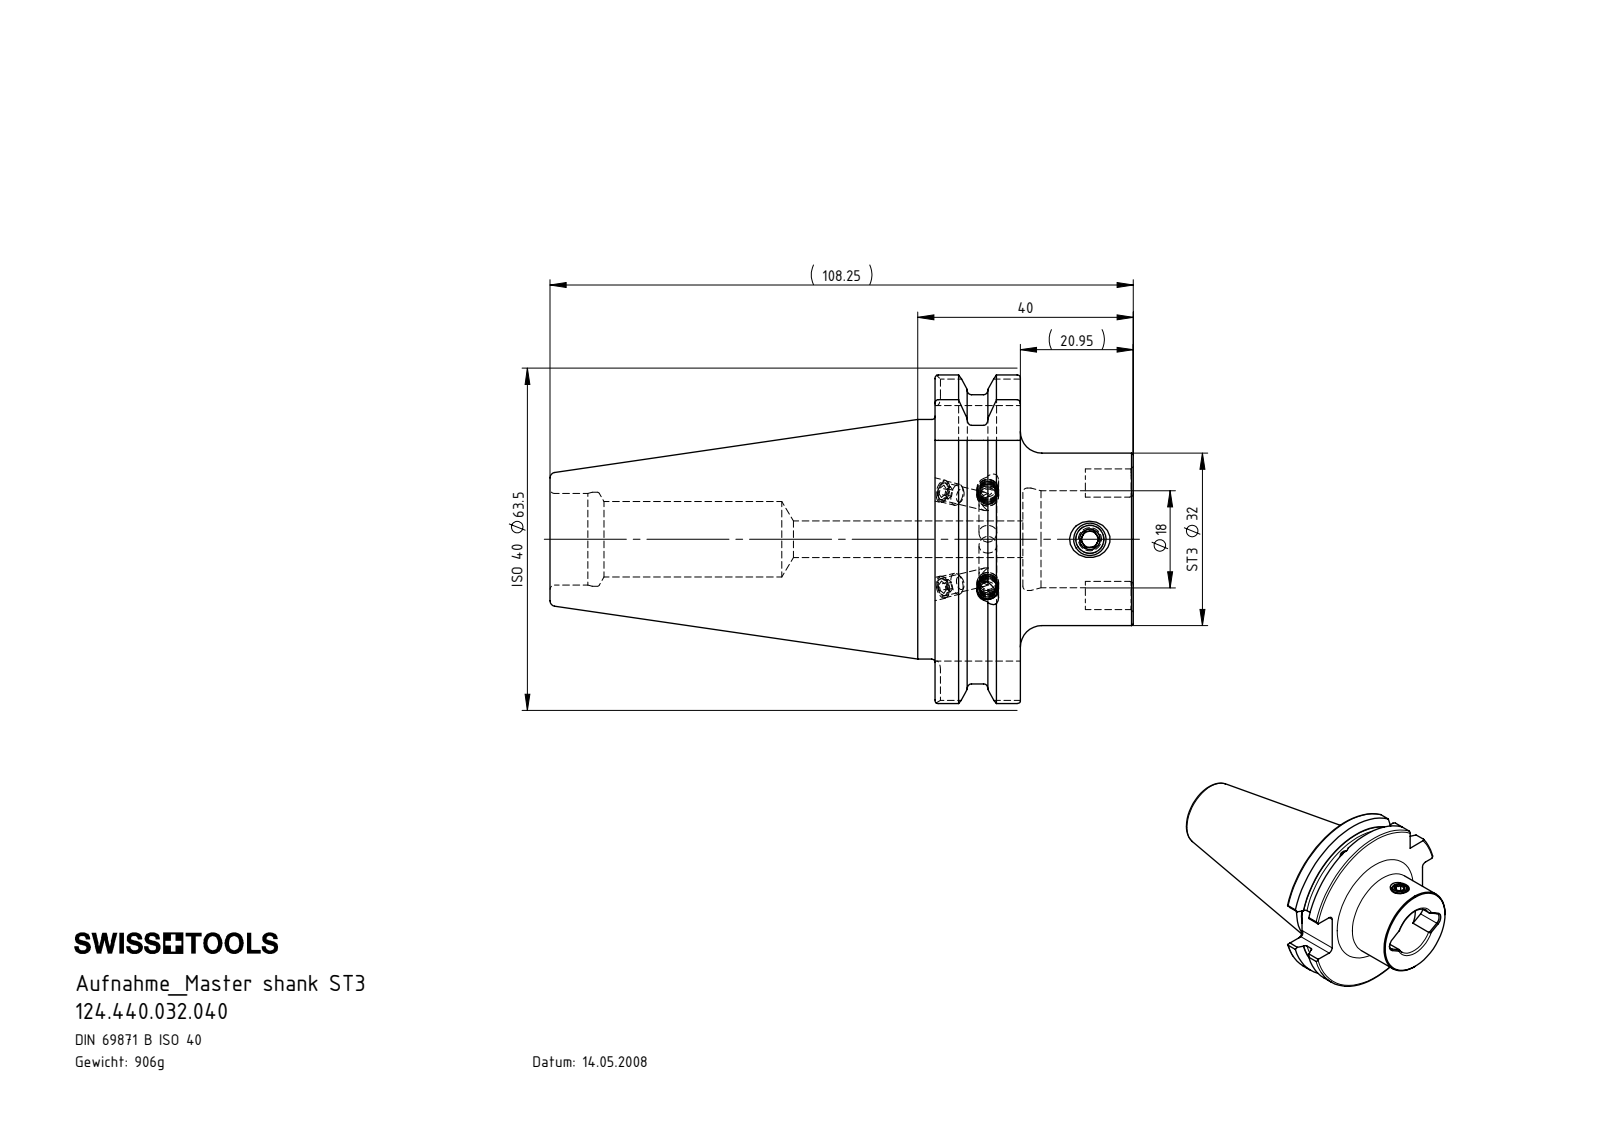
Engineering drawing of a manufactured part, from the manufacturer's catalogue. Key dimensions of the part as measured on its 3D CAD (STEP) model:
Part name (STEP PRODUCT): ST3-ER1.001.008_A; SB4.ST3.K01.040; ISO 4026 - M4 x 4_PreviewCfg; SB4-ST3.K01.040_C_mit Bundkhlung (+1 more)
STEP written by: SolidWorks 2017 (AUTOMOTIVE_DESIGN)
Units: millimetres
Bodies: 8 solids, 206 faces (78 planar, 50 cylindrical, 78 other)
Overall size (bounding box): 108.25 × 63.5 × 60.94
Volume: 115 424 mm³ · Surface area: 23 906 mm²
Round holes (diameter × count): ⌀3 ×3, ⌀3.3 ×3, ⌀4.2 ×2, ⌀4 ×1, ⌀5.25 ×1, ⌀6.8 ×1, ⌀14 ×1, ⌀17 ×1, ⌀17.45 ×1, ⌀18 ×1, ⌀19 ×1
Round bosses / shafts (diameter × count): ⌀4 ×4, ⌀44.45 ×1, ⌀32 ×1, ⌀6 ×1
Partial cylindrical surfaces — rounded edges, fillets, slot ends (radius × count): R1.6 ×8, R2.5 ×2, R28 ×1, R31.75 ×1
Main face-to-face distances: 15.85, 36.8, 20.95, 47.4, 16.3, 0.45, 20.5, 71.45, 87.3, 87.75
